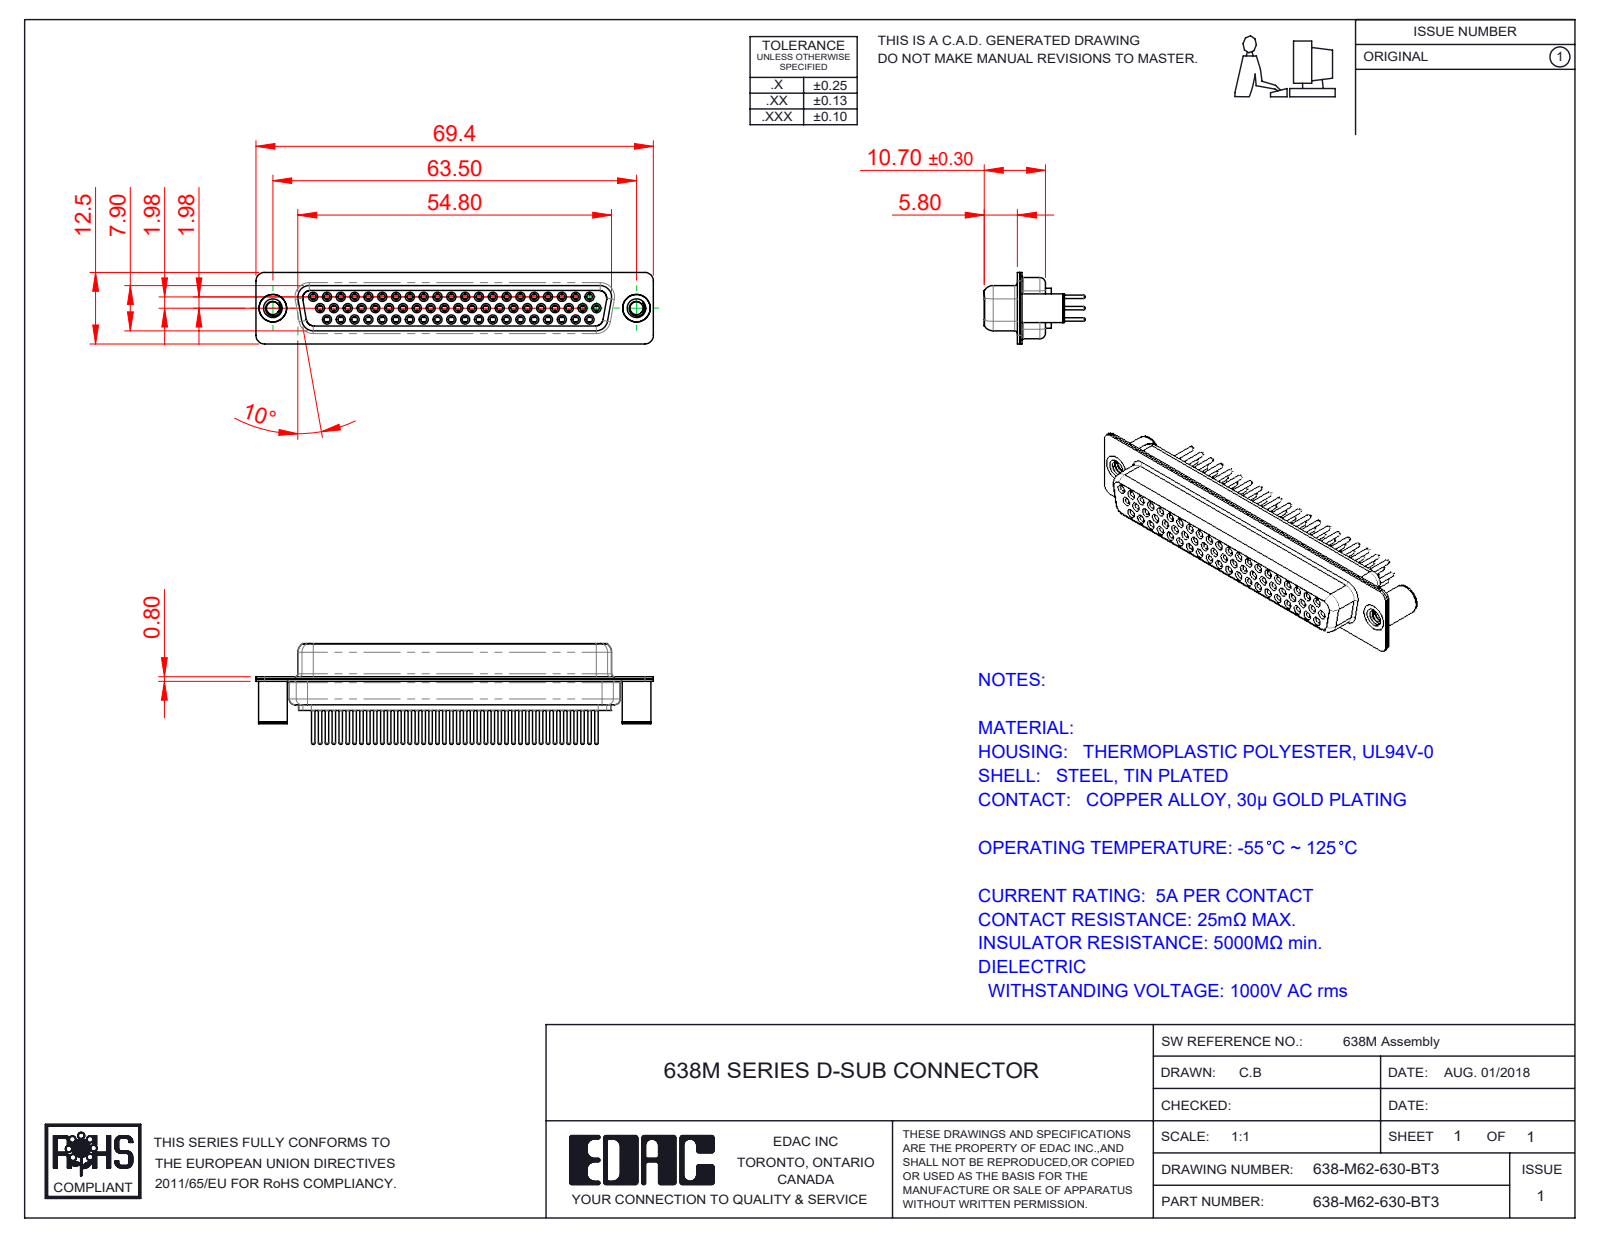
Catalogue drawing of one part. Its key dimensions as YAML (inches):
part_name: "638M Shell Rear_62 Contacts; 638M Shell Front_62 Contacts; 638M Contact Row 1_30; 638M 4-40 Threaded Board Spacer (+4 more)"
step_written_by: "SolidWorks 2020 (CONFIG_CONTROL_DESIGN)"
units: inches
bodies: {solids: 67, faces: 3723, planar: 997, cylindrical: 1339, other: 1387}
overall_size: [2.732, 0.693, 0.492]
volume: 0.312
surface_area: 25.88
round_holes:
  - {diameter: 0.039, count: 62}
  - {diameter: 0.043, count: 62}
  - {diameter: 0.067, count: 62}
  - {diameter: 0.071, count: 62}
  - {diameter: 0.079, count: 62}
  - {diameter: 0.089, count: 2}
  - {diameter: 0.128, count: 2}
  - {diameter: 0.157, count: 2}
  - {diameter: 0.189, count: 2}
round_bosses_or_shafts:
  - {diameter: 0.087, count: 62}
  - {diameter: 0.063, count: 62}
  - {diameter: 0.059, count: 62}
  - {diameter: 0.024, count: 62}
  - {diameter: 0.197, count: 2}
  - {diameter: 0.193, count: 2}
partial_cylinders:
  - {radius: 0.059, count: 16}
  - {radius: 0.079, count: 12}
  - {radius: 0.053, count: 8}
  - {radius: 0.063, count: 8}
  - {radius: 0.01, count: 4}
  - {radius: 0.02, count: 4}
  - {radius: 0.024, count: 4}
  - {radius: 0.026, count: 4}
face_to_face_distances: [0.016, 0.055, 0.018, 0.333, 0.35, 0.071, 0.039, 0.244, 0.278, 0.073]
hole_center_spacings: [0.285, 0.091, 0.095, 0.163, 0.38, 0.19, 0.57, 0.665]
